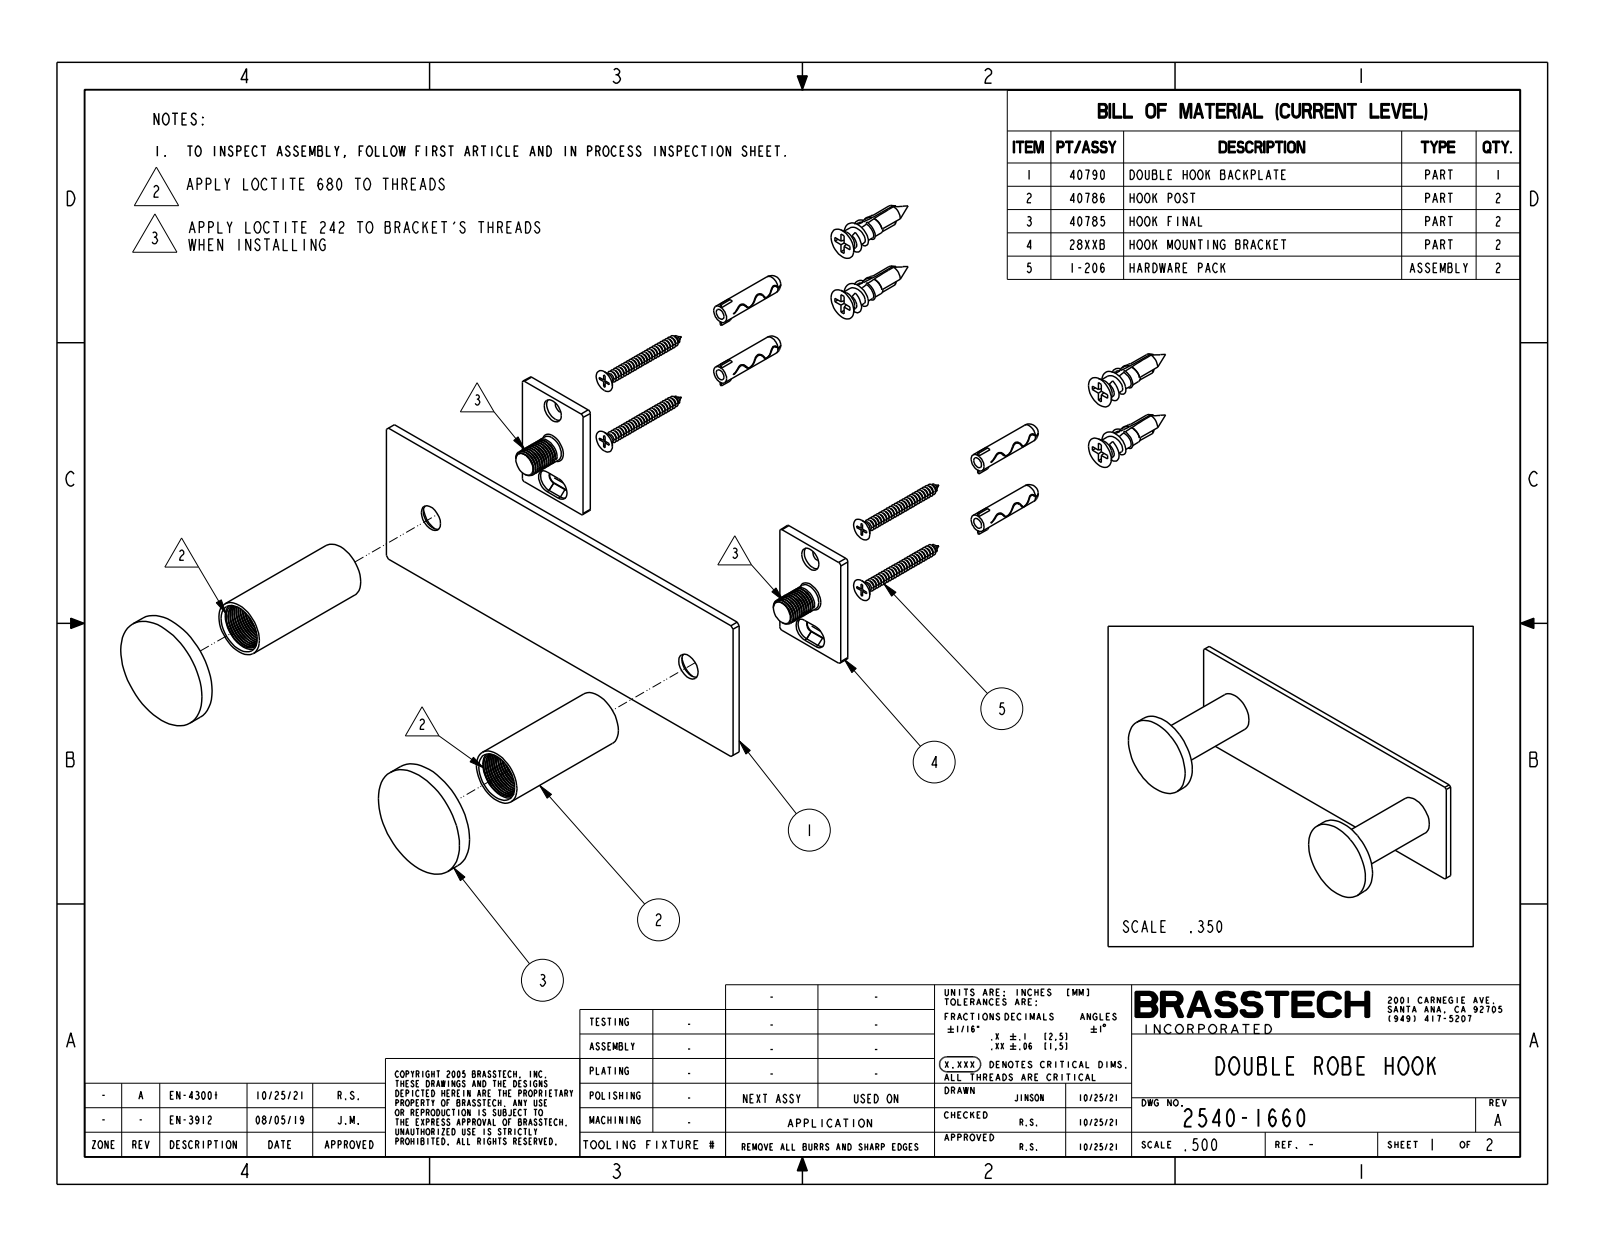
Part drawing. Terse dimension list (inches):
name: 2540-1660
written by: CREO PARAMETRIC BY PTC INC, 2018400 (CONFIG_CONTROL_DESIGN)
unit: in
bodies: 1 solid, 22 faces (14 planar, 8 cylindrical, 0 other)
size: 6.732 × 2.283 × 2.205
volume: 4.435 in³; area: 49.31 in²
bosses: 2× ⌀1.575, 2× ⌀0.787
face distances: 0.118, 2.283, 2.165, 2.087, 1.969, 0.197, 2.205, 6.732, 6.263
